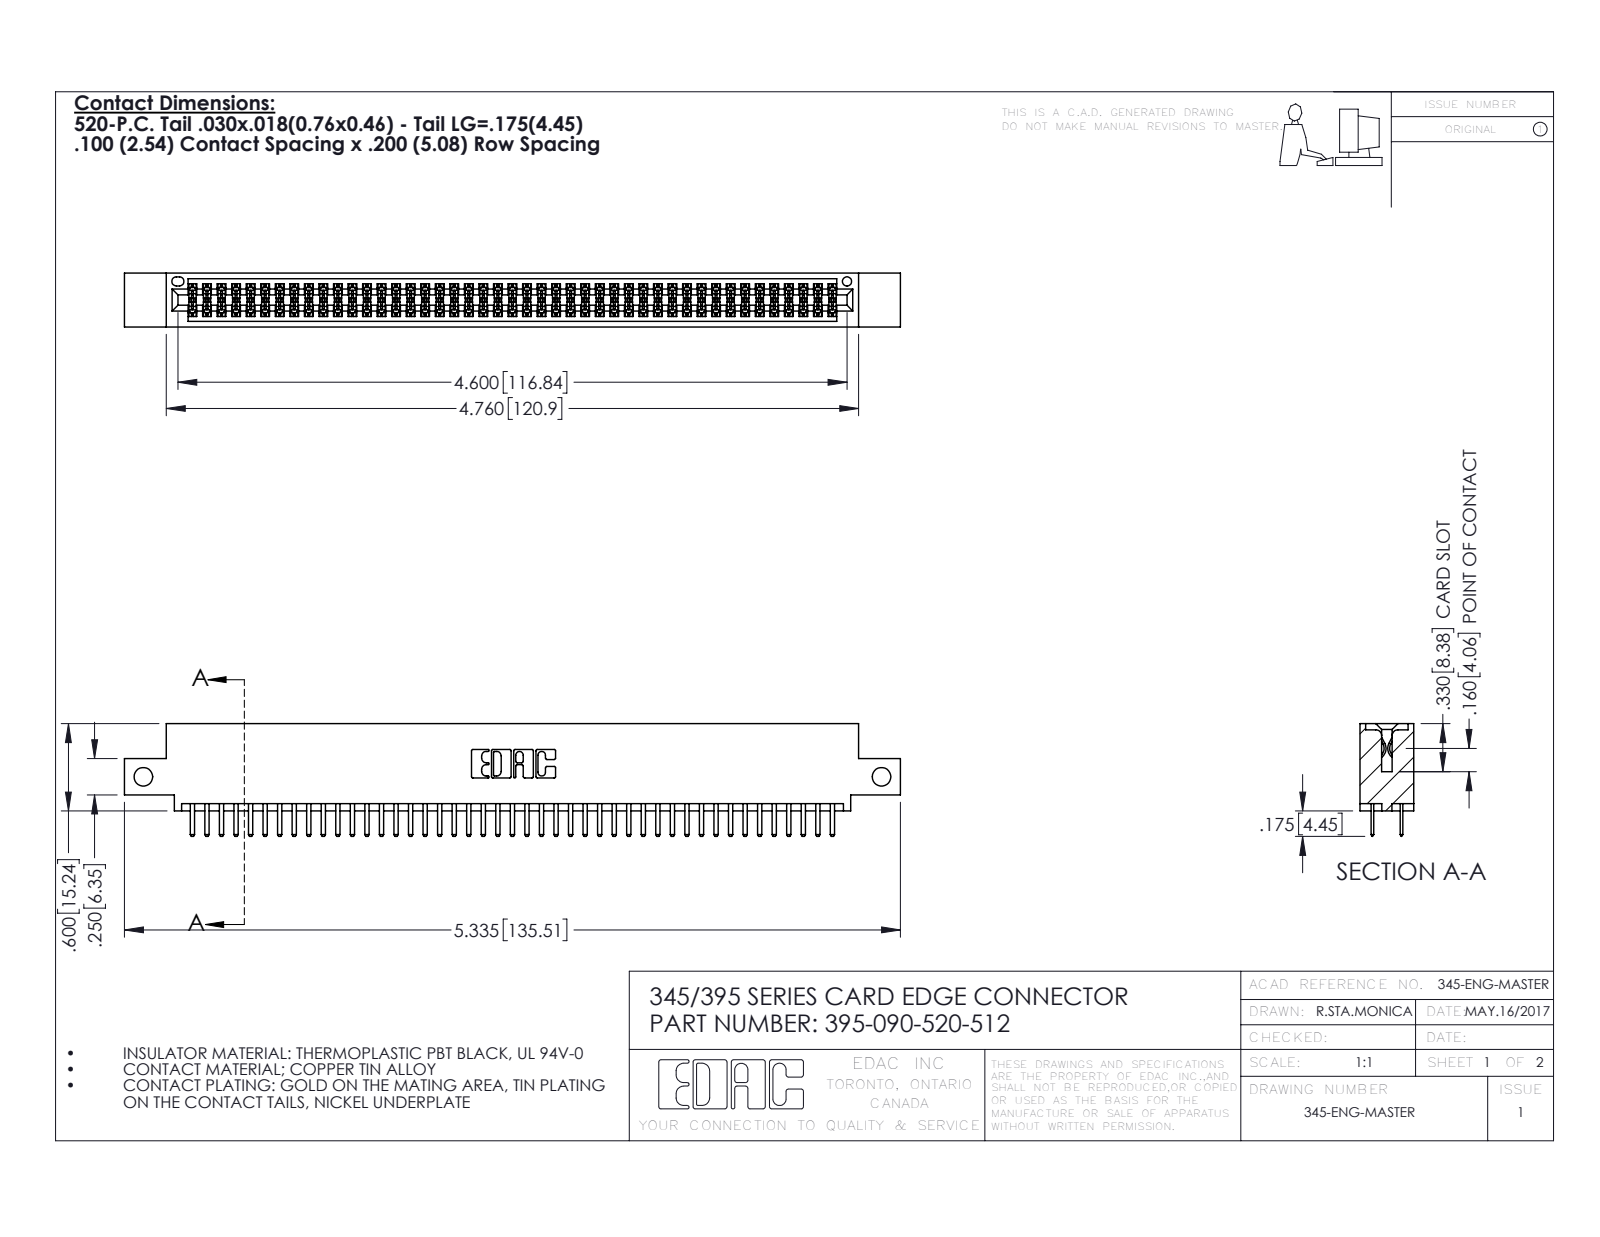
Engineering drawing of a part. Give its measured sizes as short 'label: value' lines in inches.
name: 345-292-001_345-293-120; 395-090-520-512; 345 Part_0.110 Offset - Side Mount
written by: SolidWorks 2016 (CONFIG_CONTROL_DESIGN)
unit: in
bodies: 91 solids, 4990 faces (3234 planar, 1756 cylindrical, 0 other)
size: 5.335 × 0.775 × 0.37
volume: 0.793 in³; area: 29.66 in²
holes: 2× ⌀0.128, 1× ⌀0.064
rounds: 135× R0.006, 94× R0.01, 22× R0.01, 6× R0.007, 6× R0.031, 3× R0.026, 2× R0.014, 2× R0.019
face distances: 0.298, 0.072, 0.2, 0.37, 0.098, 0.272, 0.025, 0.225, 0.022, 0.072
hole spacings: 5.075
